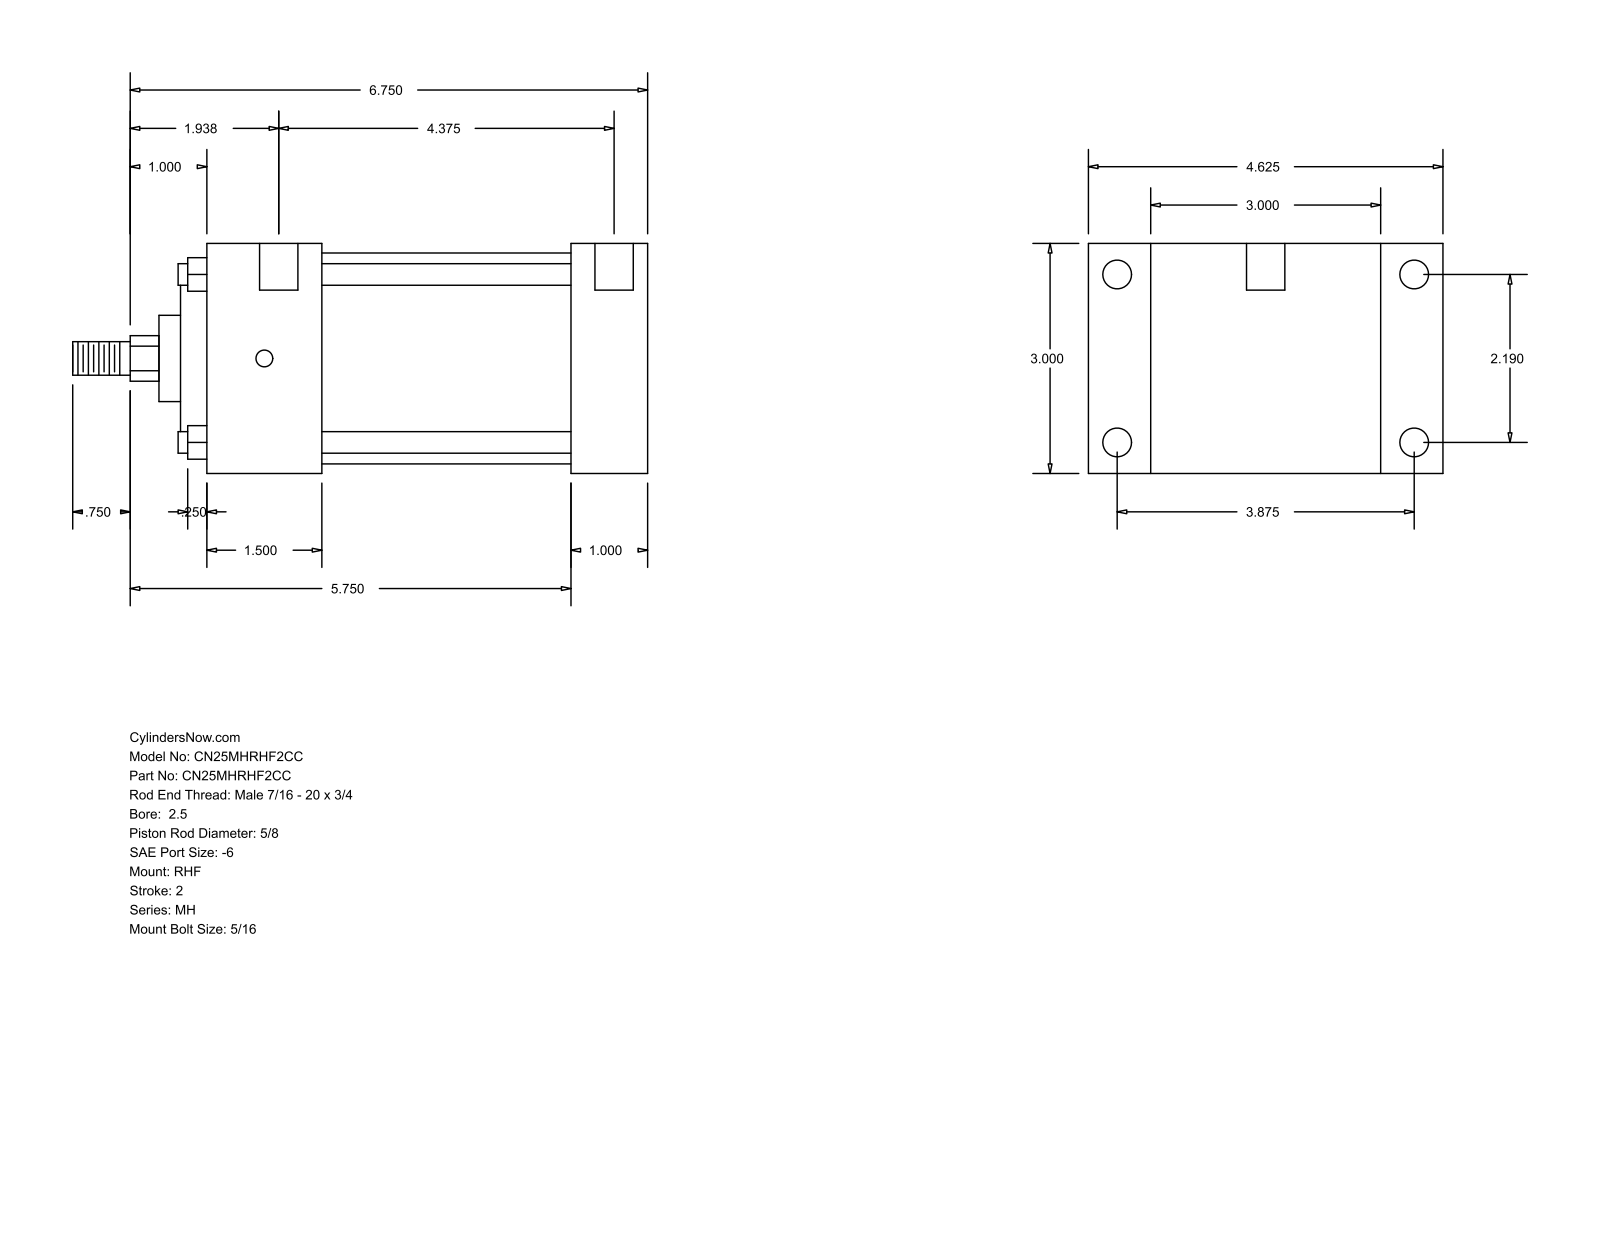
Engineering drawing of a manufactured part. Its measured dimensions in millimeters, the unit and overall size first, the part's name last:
Units: millimetres
Overall size (bounding box): 190.5 × 117.47 × 76.2
Round holes (diameter × count): ⌀5.56 ×4, ⌀9.53 ×4, ⌀12.7 ×2
Round bosses / shafts (diameter × count): ⌀7.14 ×4, ⌀69.85 ×1, ⌀55.55 ×1, ⌀28.57 ×1, ⌀15.88 ×1, ⌀11.11 ×1
Partial cylindrical surfaces — rounded edges, fillets, slot ends (radius × count): R7.54 ×1
Main face-to-face distances: 76.2, 25.4, 20.64, 96.84, 146.05, 120.65, 38.1, 82.55, 117.48, 107.95
Hole centre spacings: 55.62, 98.42, 113.05, 119.06, 3.17, 4.76, 111.13, 114.3
Bodies: 0 solids, 90 faces (61 planar, 29 cylindrical, 0 other)
Part name (STEP PRODUCT): MH_RHF__0250_0.625
STEP written by: GSSL Pune (CONFIG_CONTROL_DESIGN)
